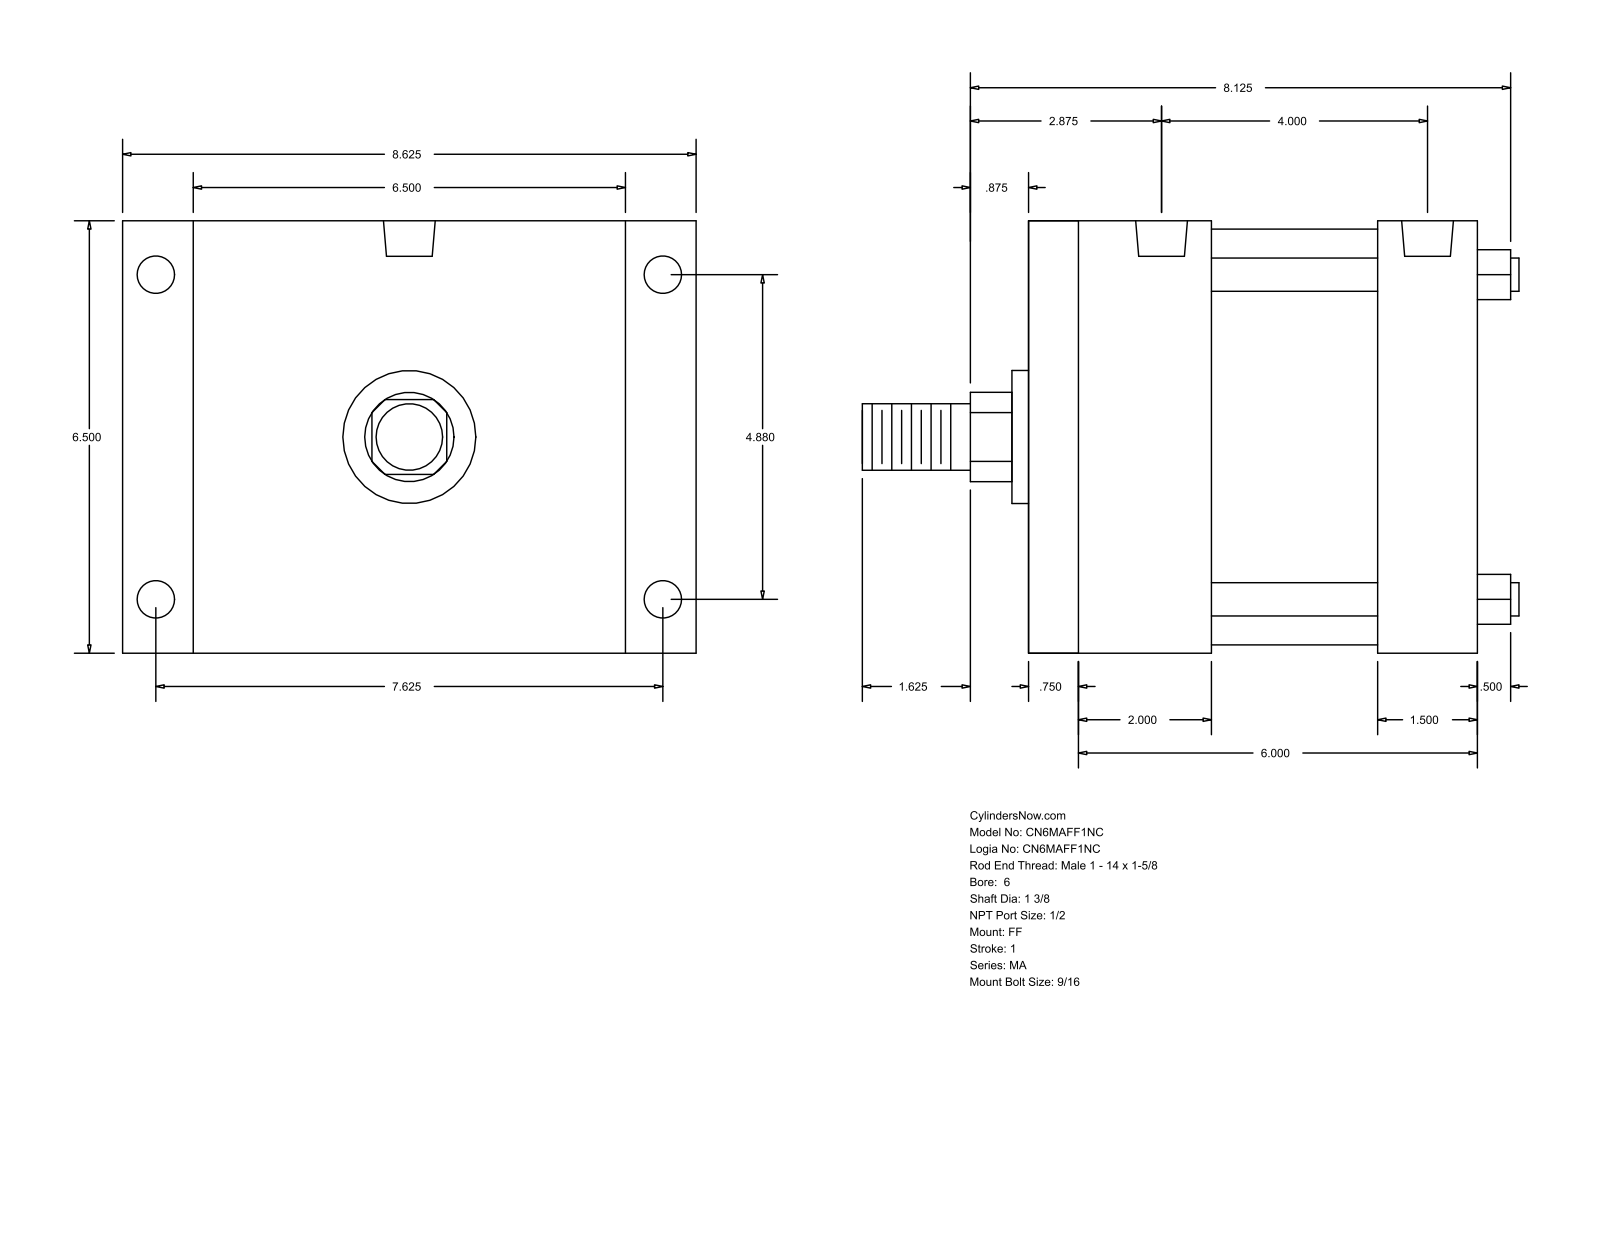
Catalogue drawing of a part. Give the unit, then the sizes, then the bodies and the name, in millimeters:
Units: millimetres
Overall size (bounding box): 250.82 × 219.07 × 165.1
Round holes (diameter × count): ⌀14.29 ×4, ⌀17.46 ×4, ⌀19.77 ×2
Round bosses / shafts (diameter × count): ⌀12.7 ×4, ⌀158.75 ×1, ⌀50.8 ×1, ⌀34.92 ×1, ⌀25.4 ×1
Partial cylindrical surfaces — rounded edges, fillets, slot ends (radius × count): R17.06 ×1
Main face-to-face distances: 165.1, 171.45, 66.67, 15.87, 155.58, 50.8, 104.78, 133.34, 117.47, 38.11
Hole centre spacings: 104.77, 123.96, 193.68, 229.95, 3.18, 101.59
Bodies: 0 solids, 92 faces (64 planar, 28 cylindrical, 0 other)
Part name (STEP PRODUCT): MA_FF__0600_1.375
STEP written by: GSSL Pune (CONFIG_CONTROL_DESIGN)
